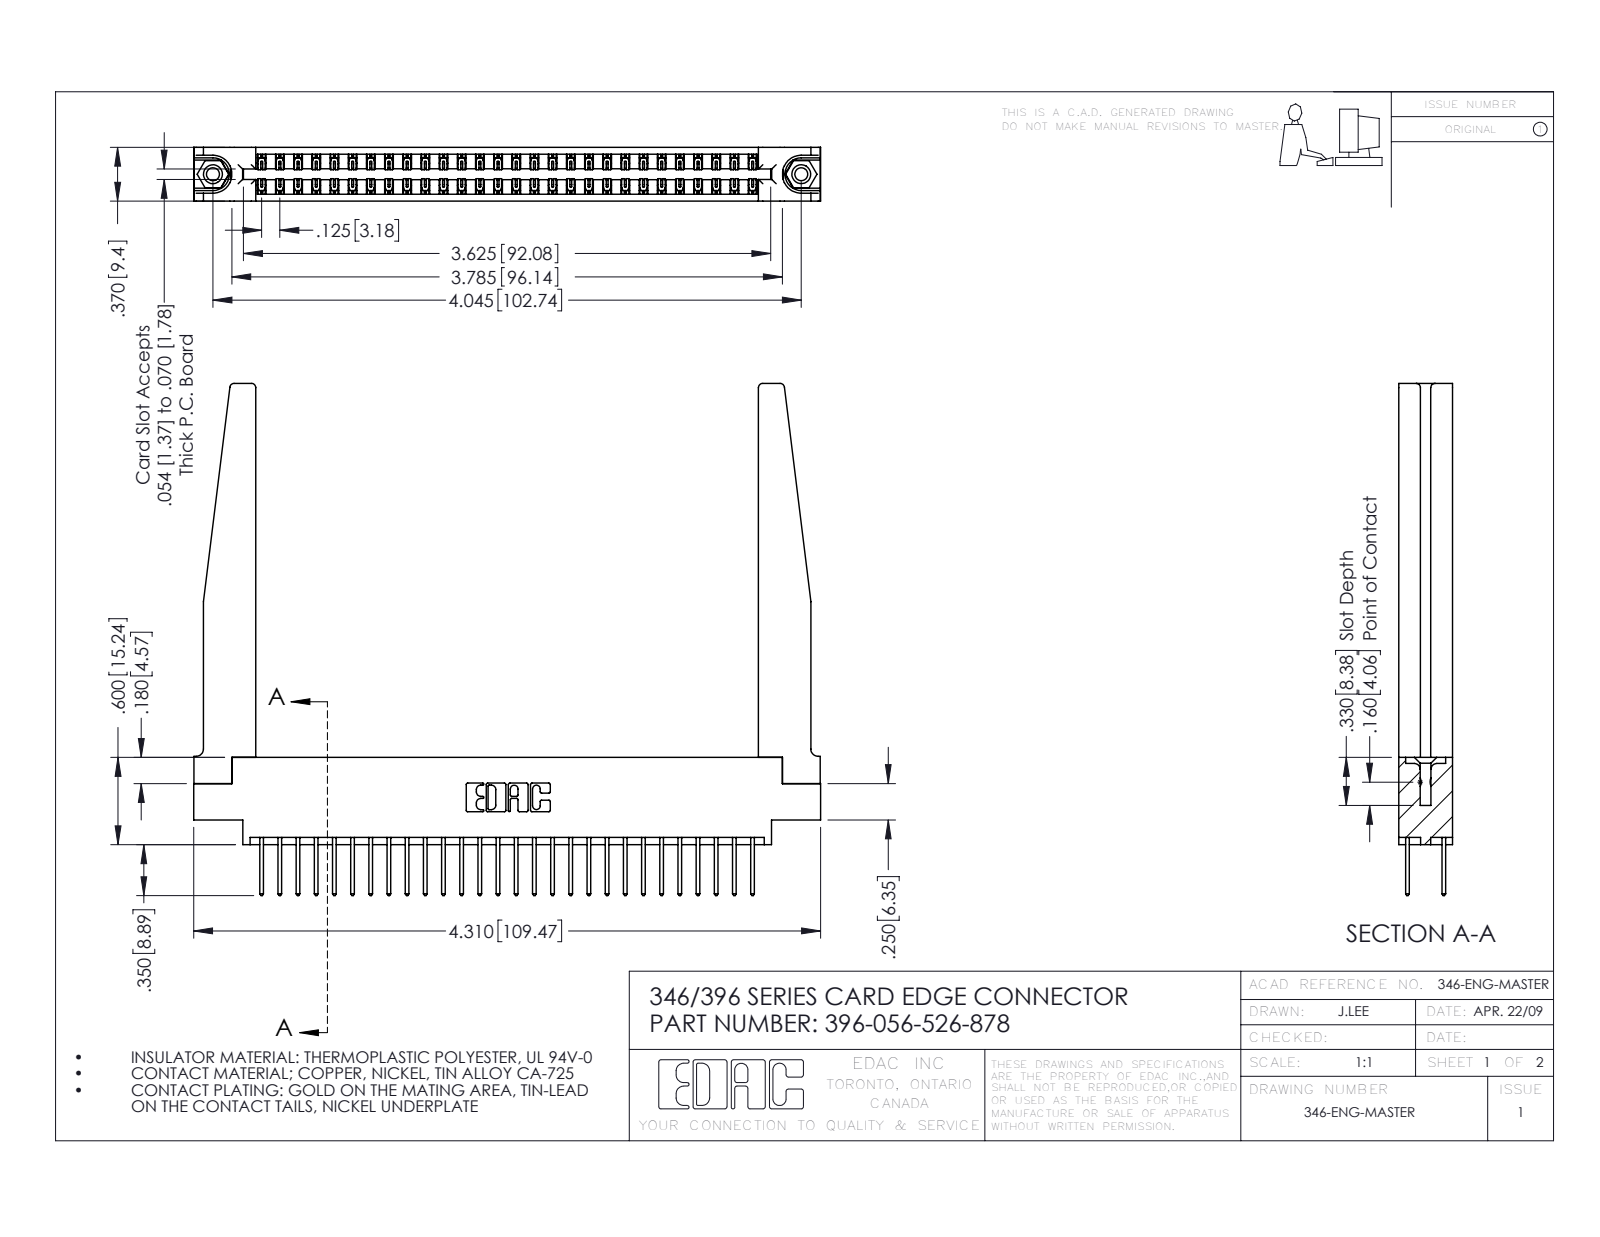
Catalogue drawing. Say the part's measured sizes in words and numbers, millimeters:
The part is named "345-292-001_345-293-126; 345-250-001_345-250-001-102; 346 Part_0.170 Offset - 0.156 Dia-TH; 346-220-078_345-220-078 (+1 more)". Its 3-D file was written by "SolidWorks 2016 (CONFIG_CONTROL_DESIGN)". It is 61 solids with 3272 faces: 2182 planar, 1038 cylindrical and 52 other. Overall it measures 109.5 by 89.4 by 9.4 millimeters. Its volume is 17 420 cubic millimeters and its surface area 21 350 square millimeters. Round holes: 2 of diameter 2.3, 2 of diameter 3.2, 2 of diameter 4, 1 of diameter 1.6. Round bosses or shafts: 2 of diameter 3.9. Partial cylindrical surfaces (rounded edges, fillets, slot ends): 84 of radius 0.2, 56 of radius 0.3, 22 of radius 0.3, 8 of radius 0.8, 6 of radius 0.2, 6 of radius 0.8, 3 of radius 0.7, 2 of radius 0.4. The main face-to-face distances are 9.4, 1.2, 8.2, 1.8, 6.4, 3.8, 3.8, 7.6, 0.6, 7. The hole center spacings are 6.2, 97.5, 102.7.
